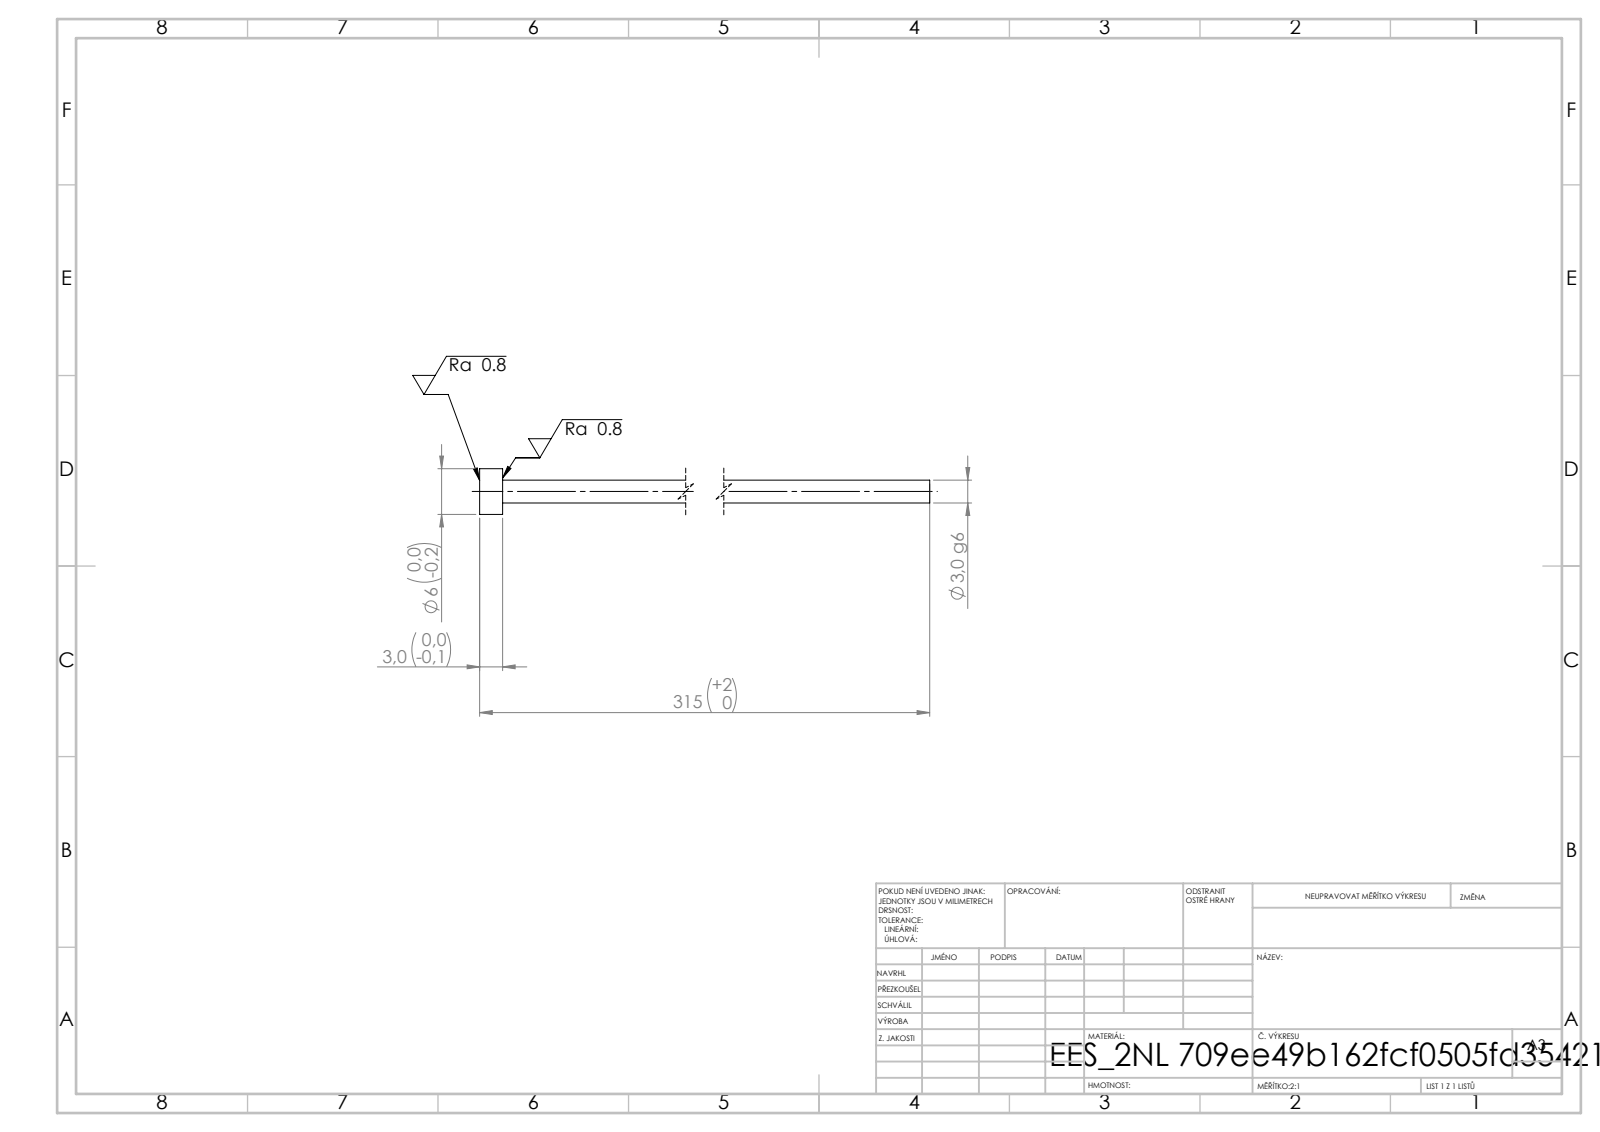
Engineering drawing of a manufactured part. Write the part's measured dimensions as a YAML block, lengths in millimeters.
step_written_by: "SolidWorks 2019 (CONFIG_CONTROL_DESIGN)"
units: millimeters
bodies: {solids: 1, faces: 7, planar: 3, cylindrical: 4, other: 0}
overall_size: [315, 6, 6]
volume: 2290
surface_area: 3054
round_bosses_or_shafts:
  - {diameter: 6, count: 1}
  - {diameter: 3, count: 1}
face_to_face_distances: [3, 315, 312]
